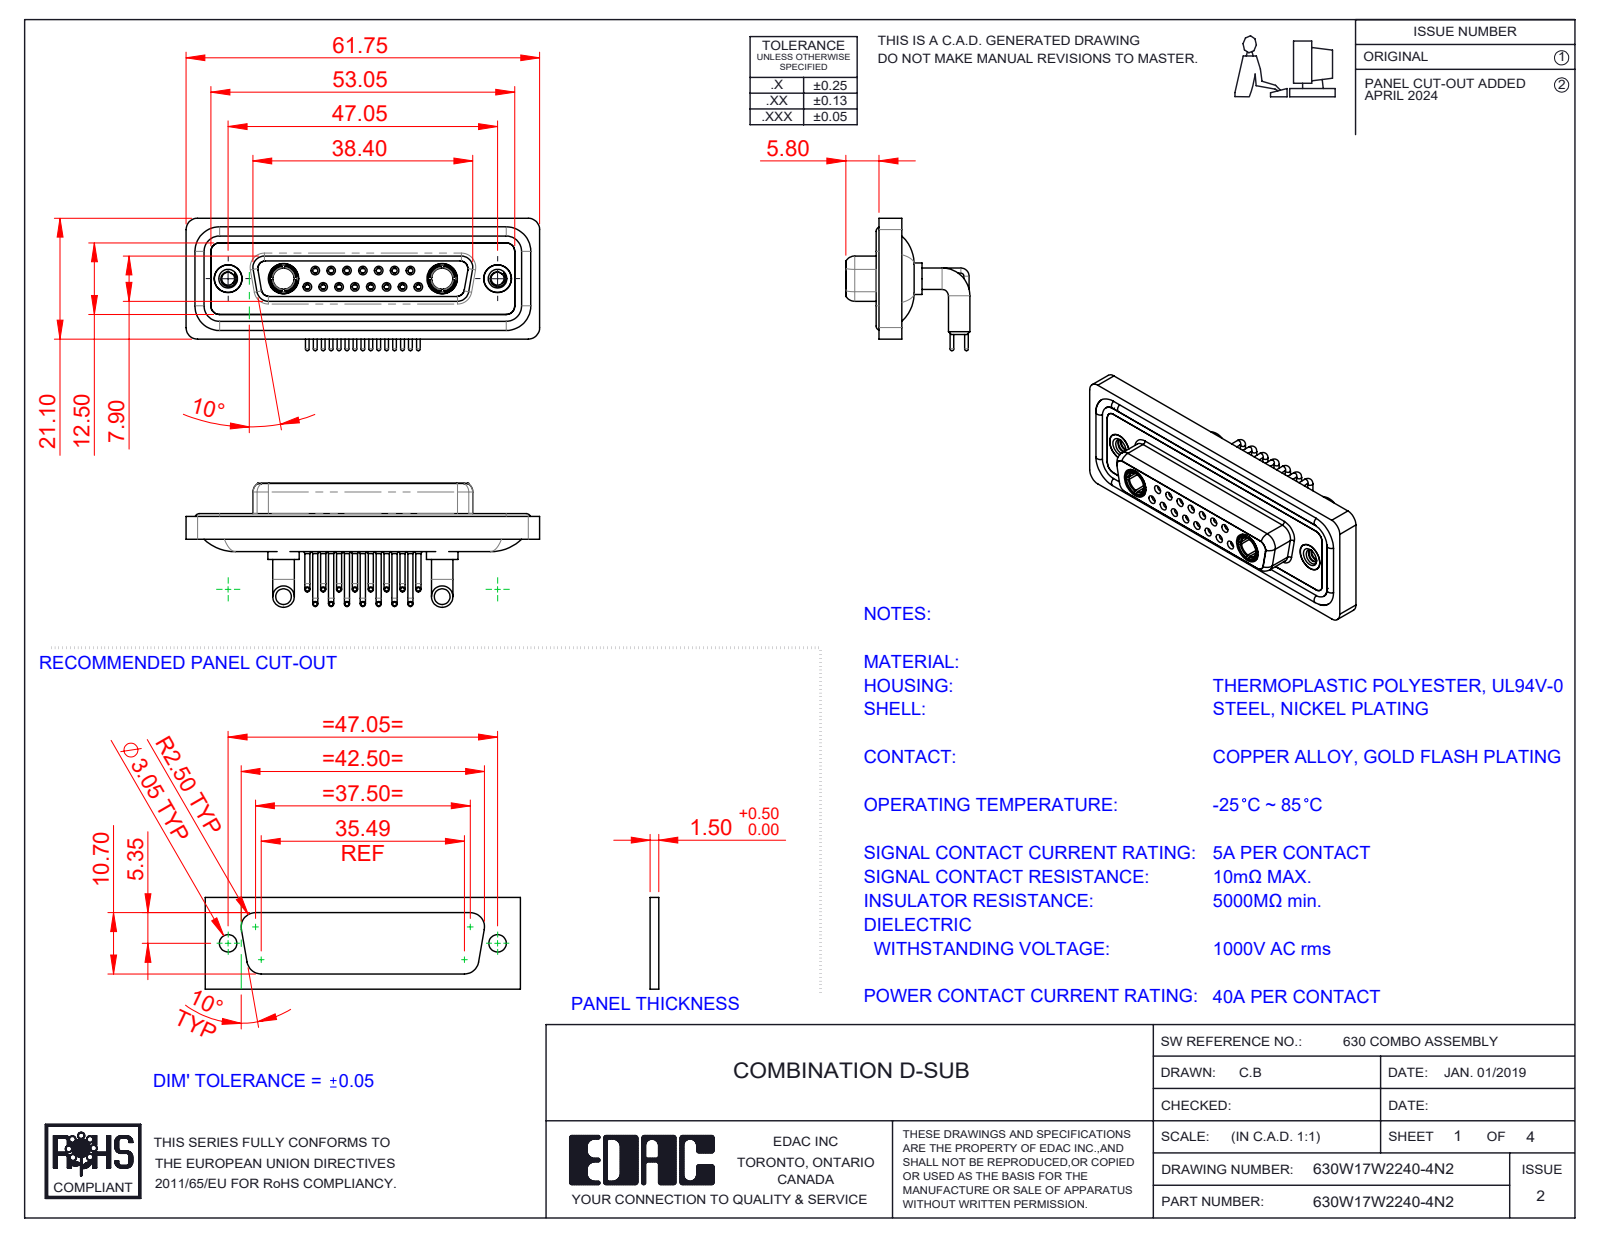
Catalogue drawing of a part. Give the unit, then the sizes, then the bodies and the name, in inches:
Units: inches
Overall size (bounding box): 2.431 × 0.91 × 0.854
Round holes (diameter × count): ⌀0.035 ×15, ⌀0.043 ×15, ⌀0.059 ×15, ⌀0.079 ×15, ⌀0.063 ×8, ⌀0.067 ×7, ⌀0.191 ×4, ⌀0.089 ×2, ⌀0.146 ×2, ⌀0.157 ×2, ⌀0.159 ×2, ⌀0.197 ×2
Round bosses / shafts (diameter × count): ⌀0.035 ×15, ⌀0.026 ×15, ⌀0.063 ×11, ⌀0.148 ×4, ⌀0.217 ×2, ⌀0.205 ×2, ⌀0.195 ×2, ⌀0.195 ×2
Partial cylindrical surfaces — rounded edges, fillets, slot ends (radius × count): R0.059 ×18, R0.079 ×18, R0.053 ×8, R0.063 ×8, R0.01 ×4, R0.02 ×4, R0.024 ×4, R0.026 ×4
Main face-to-face distances: 0.016, 0.071, 0.161, 0.043, 0.063, 0.122, 0.098, 0.059, 0.146, 0.055
Hole centre spacings: 0.124, 0.109, 0.218, 0.327, 0.198, 0.295, 0.436, 0.198
Volume: 0.527 in³ · Surface area: 22.66 in²
Bodies: 26 solids, 1337 faces (388 planar, 583 cylindrical, 366 other)
Part name (STEP PRODUCT): 630Combo Threaded Rivet_2; 630Combo Waterproof Housing_25 Contacts; 630Combo Housing_17W2; Power Socket_40A RA (+5 more)
STEP written by: SolidWorks 2023 (CONFIG_CONTROL_DESIGN)
